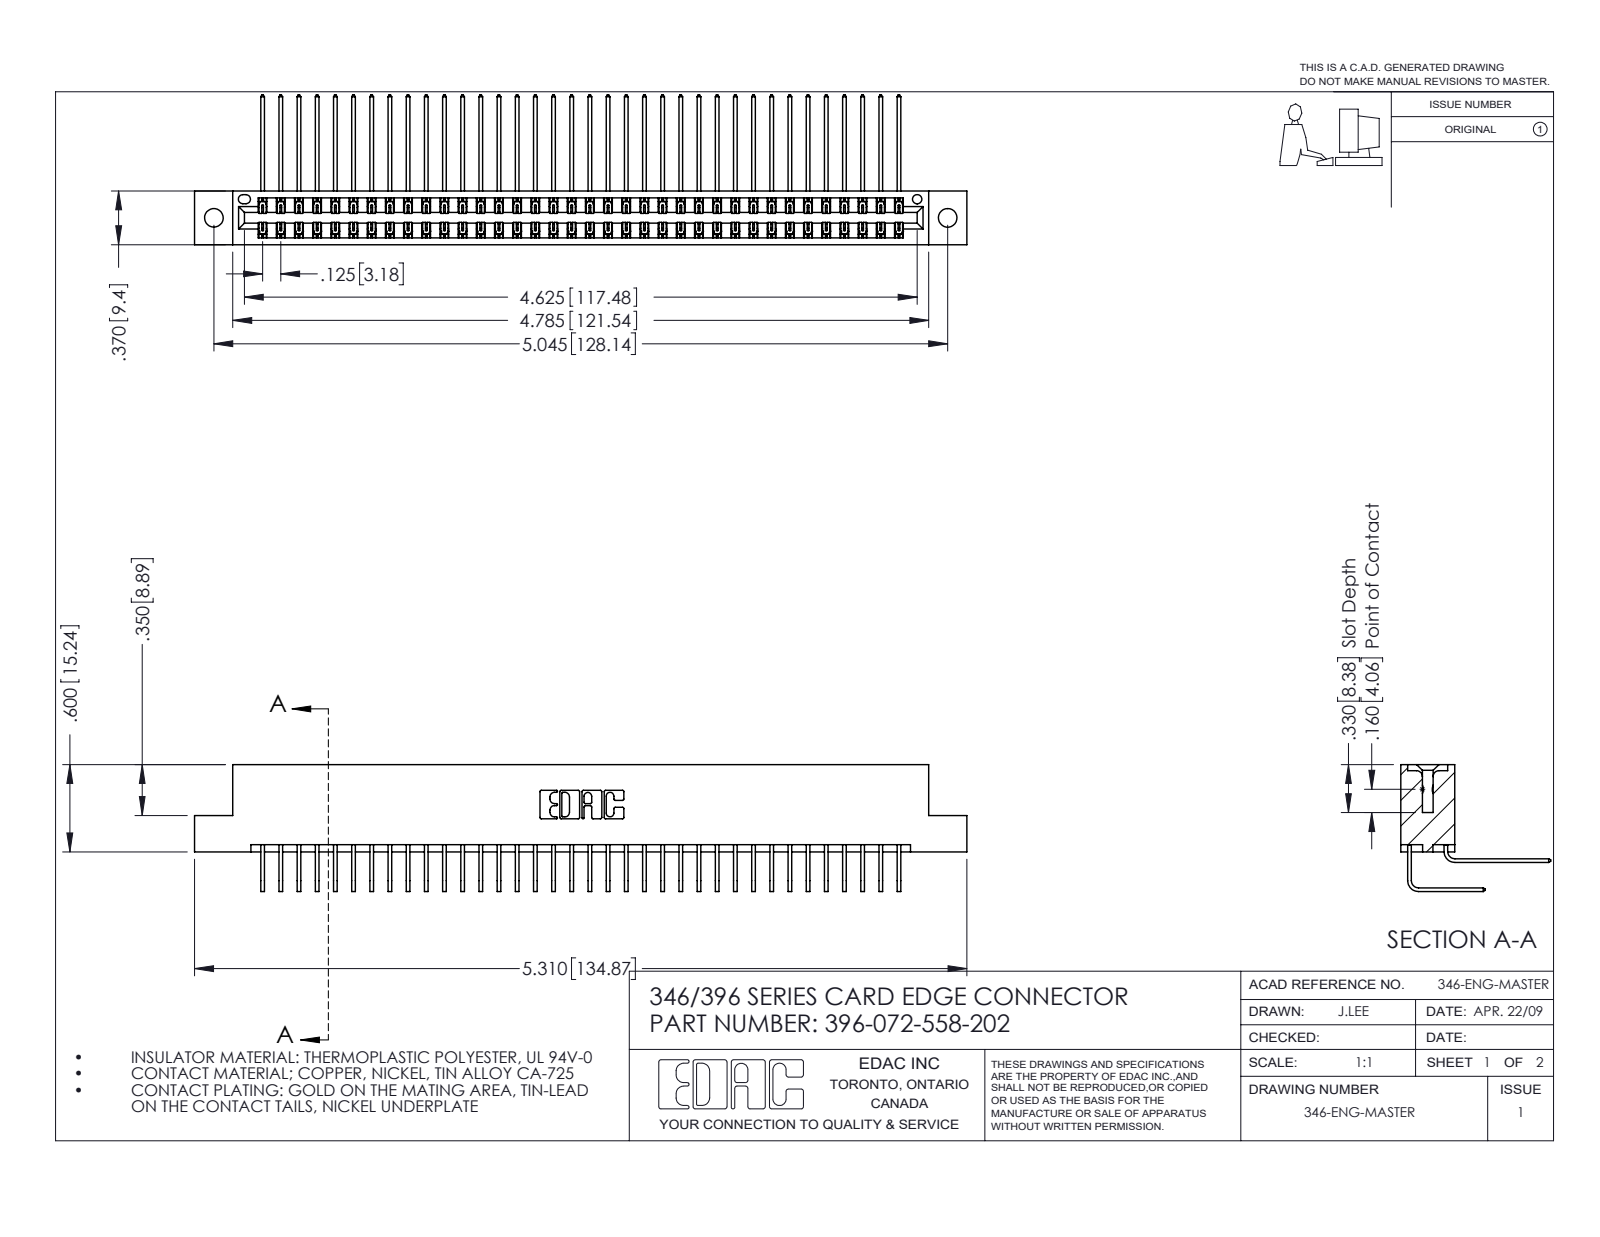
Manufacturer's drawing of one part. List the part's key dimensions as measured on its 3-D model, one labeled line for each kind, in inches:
Part name (STEP PRODUCT): 346 Part_Flush Mounting Lugs - 0.128 Dia; 345-292-001_558 Tail - 2; 345-292-001_558 559 Tail - 1; 396-072-558-202
STEP written by: SolidWorks 2016 (CONFIG_CONTROL_DESIGN)
Units: inches
Bodies: 73 solids, 4010 faces (2740 planar, 1270 cylindrical, 0 other)
Overall size (bounding box): 5.31 × 1.03 × 0.873
Volume: 0.823 in³ · Surface area: 31.25 in²
Round holes (diameter × count): ⌀0.128 ×2, ⌀0.064 ×1
Partial cylindrical surfaces — rounded edges, fillets, slot ends (radius × count): R0.006 ×108, R0.01 ×22, R0.007 ×6, R0.031 ×6, R0.026 ×3, R0.014 ×2, R0.022 ×2, R0.024 ×2
Main face-to-face distances: 0.048, 0.322, 0.025, 0.37, 0.25, 0.072, 0.298, 0.275, 0.148, 0.222
Hole centre spacings: 0.246, 4.836, 5.045
